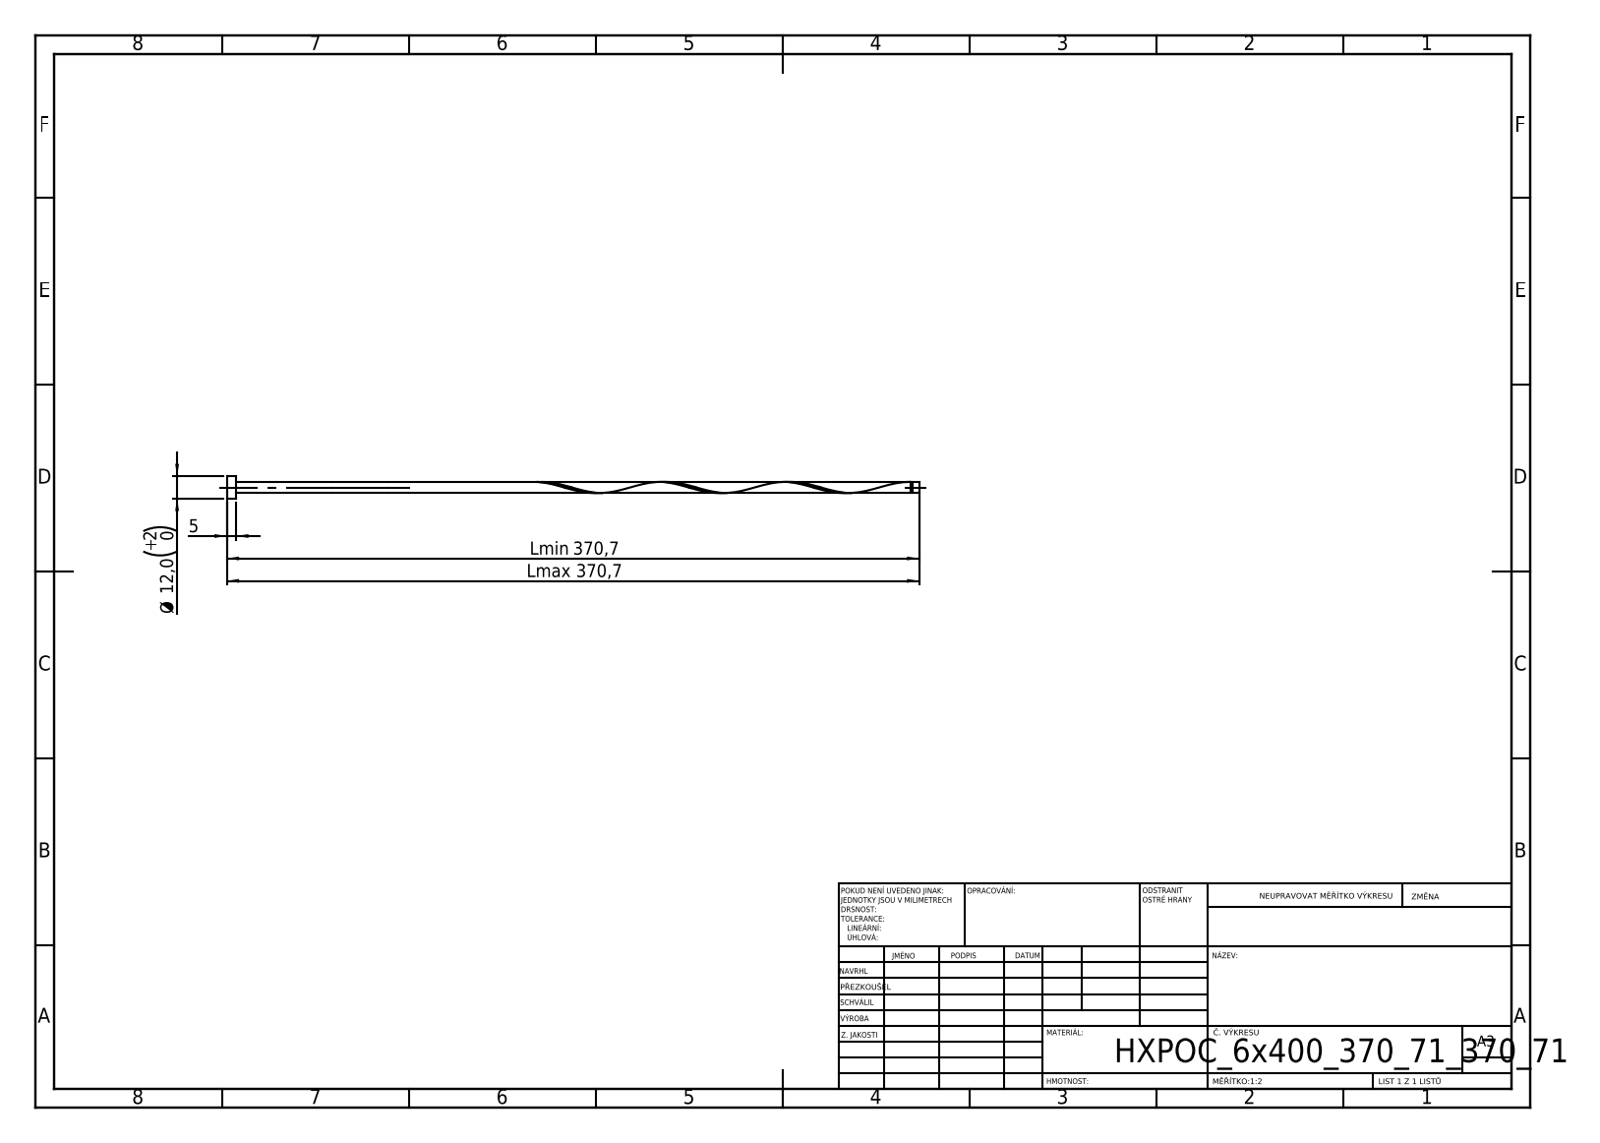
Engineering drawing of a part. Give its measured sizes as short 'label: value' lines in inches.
written by: SolidWorks 2019 (CONFIG_CONTROL_DESIGN)
unit: in
bodies: 1 solid, 16 faces (6 planar, 9 cylindrical, 1 other)
size: 14.595 × 0.472 × 0.472
volume: 0.812 in³; area: 15.43 in²
bosses: 1× ⌀0.472, 1× ⌀0.236, 1× ⌀0.189
face distances: 0.197, 14.595, 14.398, 14.454, 14.257, 0.141, 14.407, 14.21, 0.047, 0.188
